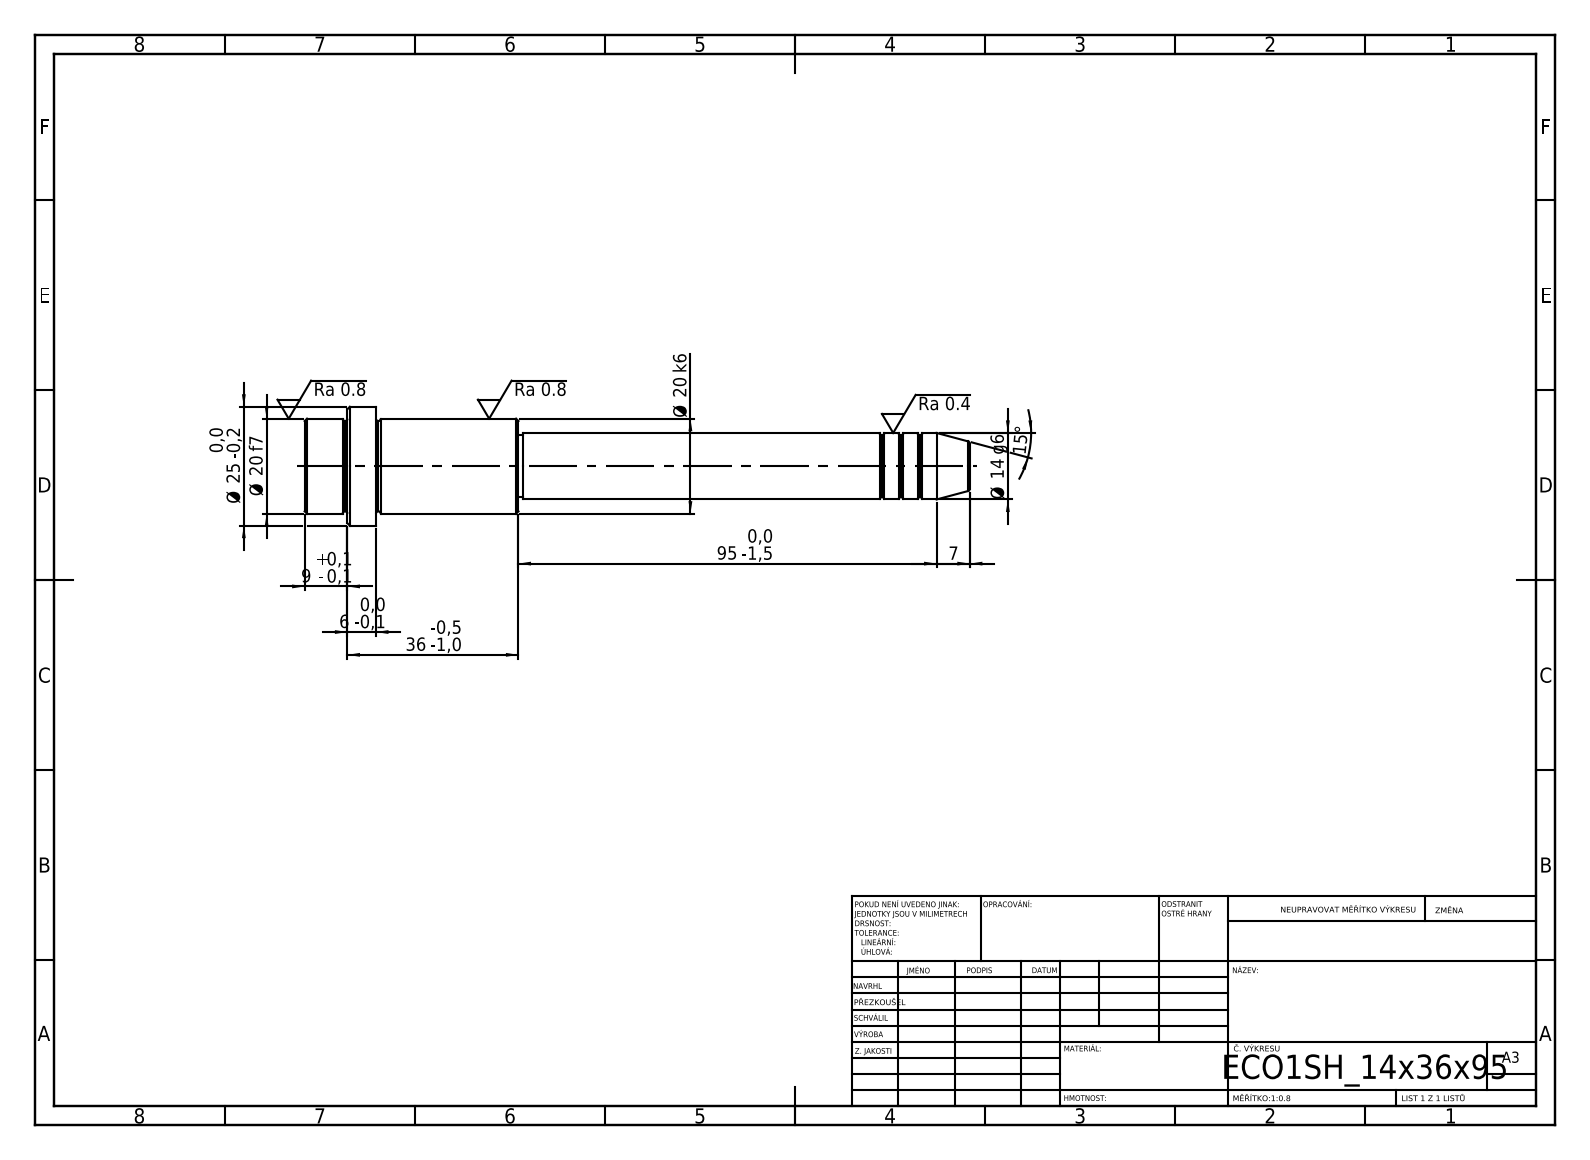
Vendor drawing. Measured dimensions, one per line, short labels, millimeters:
written by: SolidWorks 2019 (CONFIG_CONTROL_DESIGN)
unit: mm
bodies: 1 solid, 52 faces (6 planar, 16 cylindrical, 30 other)
size: 140 × 25 × 25
volume: 29 413 mm³; area: 8 085 mm²
bosses: 1× ⌀25, 1× ⌀20, 1× ⌀14, 1× ⌀13
face distances: 15, 30, 45, 36, 6, 9, 95, 125, 131, 140
